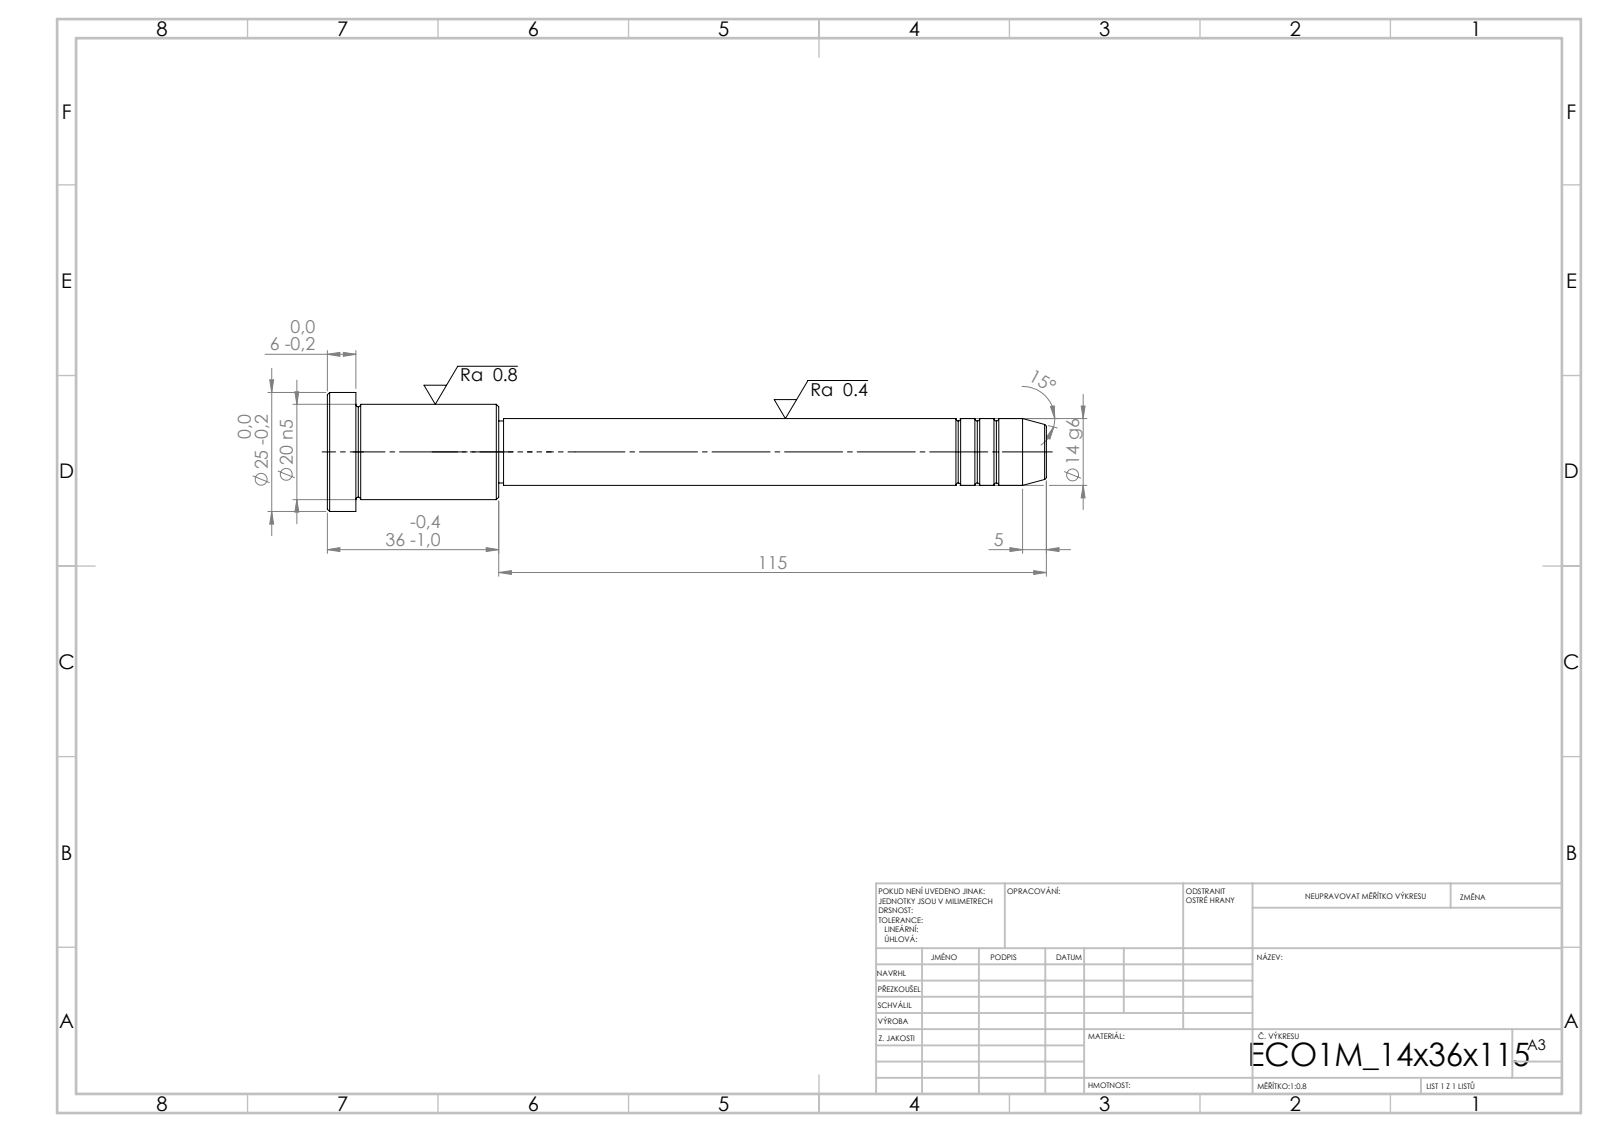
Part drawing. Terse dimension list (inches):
written by: SolidWorks 2019 (CONFIG_CONTROL_DESIGN)
unit: in
bodies: 1 solid, 43 faces (5 planar, 14 cylindrical, 24 other)
size: 5.945 × 0.984 × 0.984
volume: 1.82 in³; area: 13.05 in²
bosses: 1× ⌀0.984, 1× ⌀0.787, 1× ⌀0.551, 1× ⌀0.512
face distances: 0.236, 1.181, 1.417, 4.528, 5.709, 5.945, 4.488, 0.039, 1.22, 1.457
